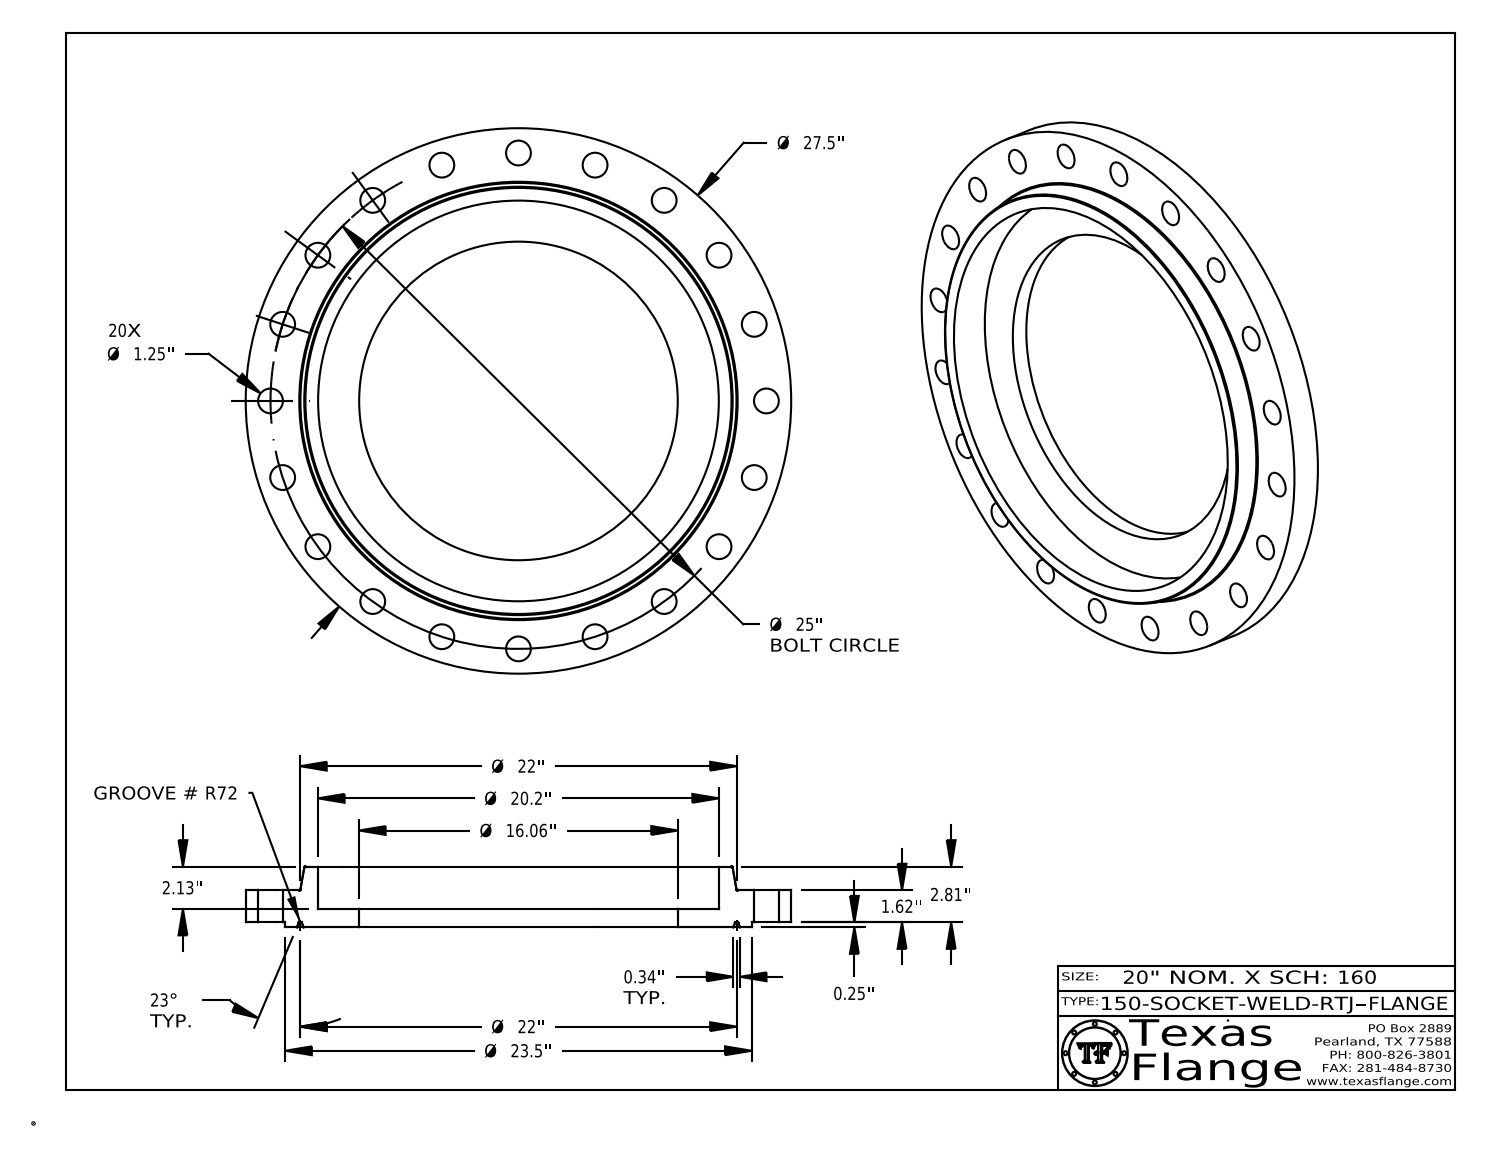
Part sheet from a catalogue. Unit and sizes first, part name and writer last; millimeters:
Units: millimetres
Overall size (bounding box): 698.5 × 698.5 × 77.7
Round holes (diameter × count): ⌀31.8 ×20, ⌀12.6 ×1, ⌀408 ×1, ⌀513.1 ×1
Round bosses / shafts (diameter × count): ⌀0.8 ×8, ⌀698.5 ×1, ⌀596.9 ×1, ⌀9.9 ×1
Main face-to-face distances: 47.5, 6.4, 41.1, 23.6, 17.3, 23.9, 77.7, 71.4, 54.1, 30.2
Hole centre spacings: 317.5, 373.2, 449, 513.7, 603.9, 627.2, 288.3, 565.8
Volume: 9 824 000 mm³ · Surface area: 832 300 mm²
Bodies: 1 solid, 454 faces (372 planar, 68 cylindrical, 14 other)
Part name (STEP PRODUCT): 150-SOCKET-WELD-RTJ
STEP written by: CATIA V5 STEP AP214 (AUTOMOTIVE_DESIGN)
